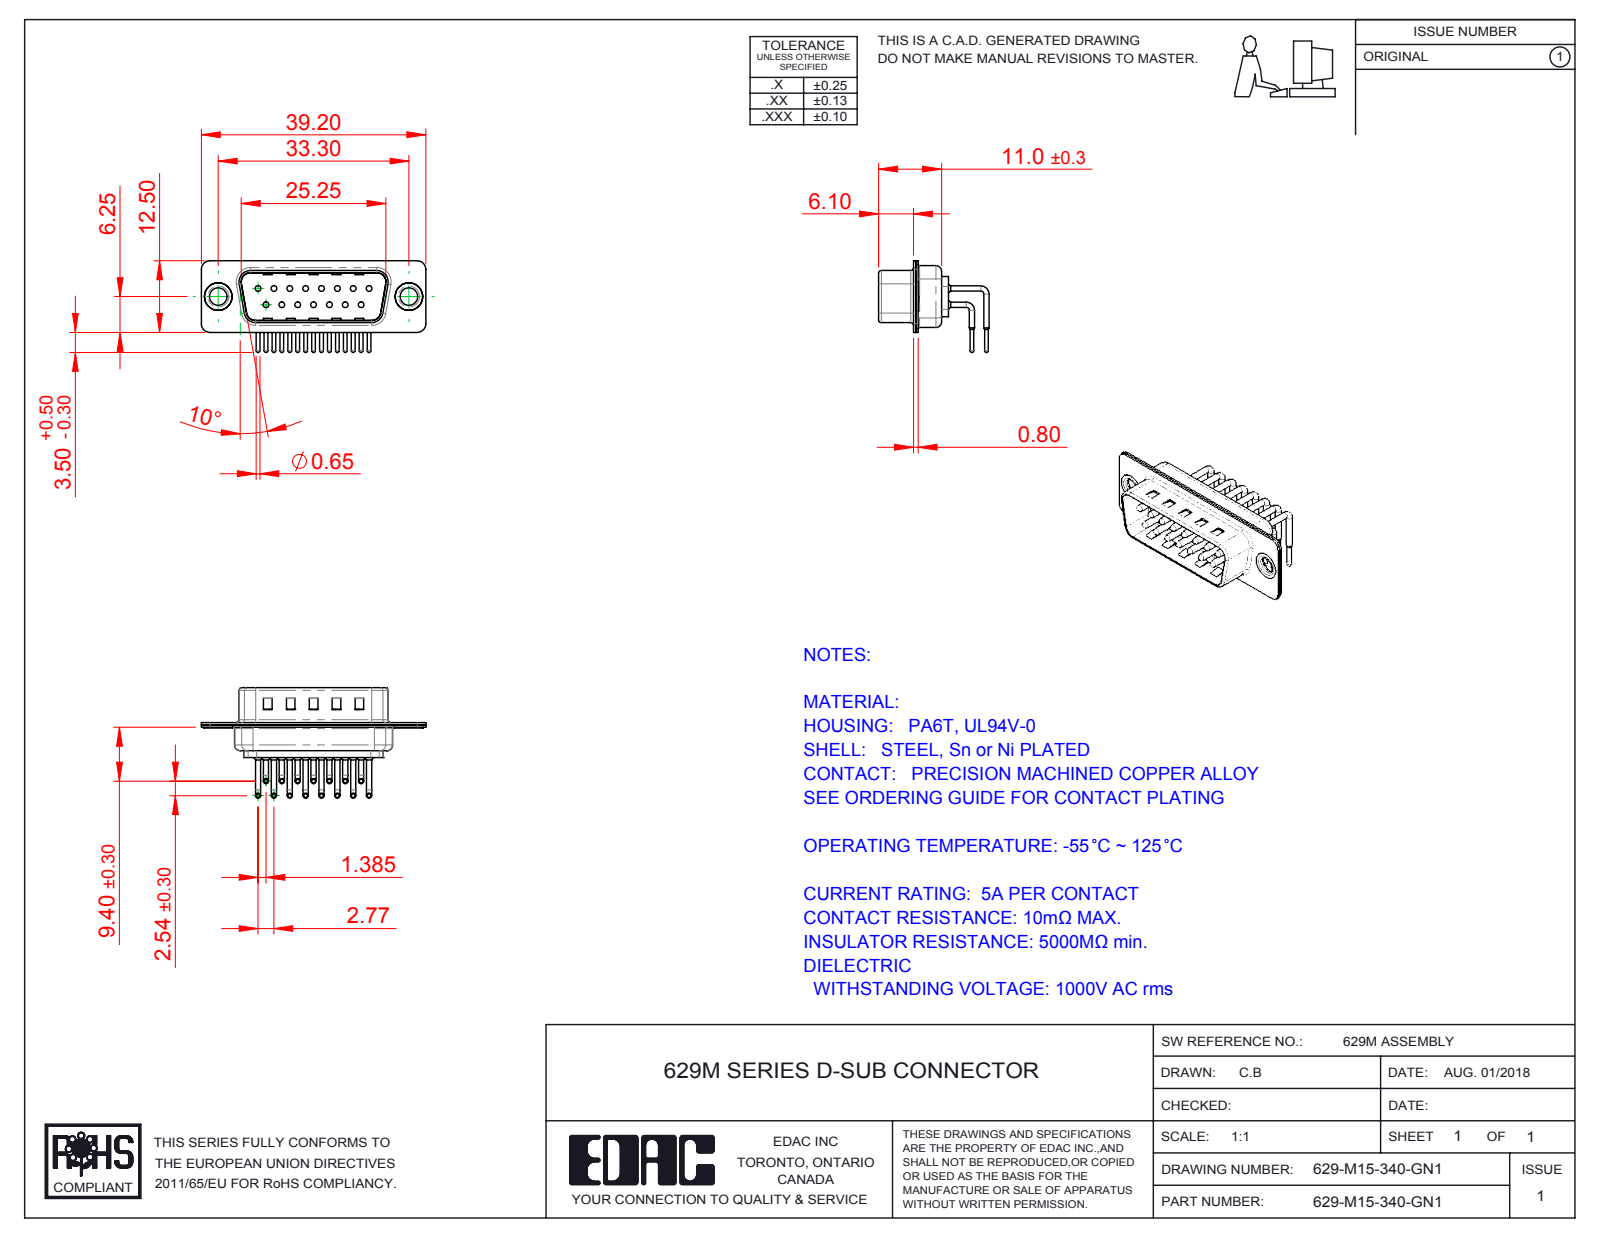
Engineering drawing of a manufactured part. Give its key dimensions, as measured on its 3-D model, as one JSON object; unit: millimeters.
{"part_name": "629-M15-340-GN1; 629M Contact Row 1; 629M Contact Row 2; 629M Thru Hole Rivet (+3 more)", "step_written_by": "SolidWorks 2016 (CONFIG_CONTROL_DESIGN)", "units": "millimeters", "bodies": {"solids": 20, "faces": 1964, "planar": 1099, "cylindrical": 657, "other": 208}, "overall_size": [39.2, 19.29, 16], "volume_mm3": 1881, "surface_area_mm2": 5213, "round_holes": [[1, 15], [1.7, 15], [2, 15], [3.05, 2], [4, 2], [4.8, 2]], "round_bosses_or_shafts": [[0.9, 30], [1.5, 15], [0.65, 15], [5, 2], [4.9, 2], [3.55, 2]], "partial_cylinders_radius": [[1.5, 16], [1.01, 15], [2, 12], [0.5, 8], [1.6, 8], [0.25, 4], [0.6, 4], [0.65, 4]], "face_to_face_distances": [0.4, 0.85, 9.55, 8.7, 1.25, 0.8, 10.4, 1.5, 0.35, 1.9], "hole_center_spacings": [3.16, 2.77, 5.54, 8.31, 11.08, 5.03, 5.04, 7.48]}
